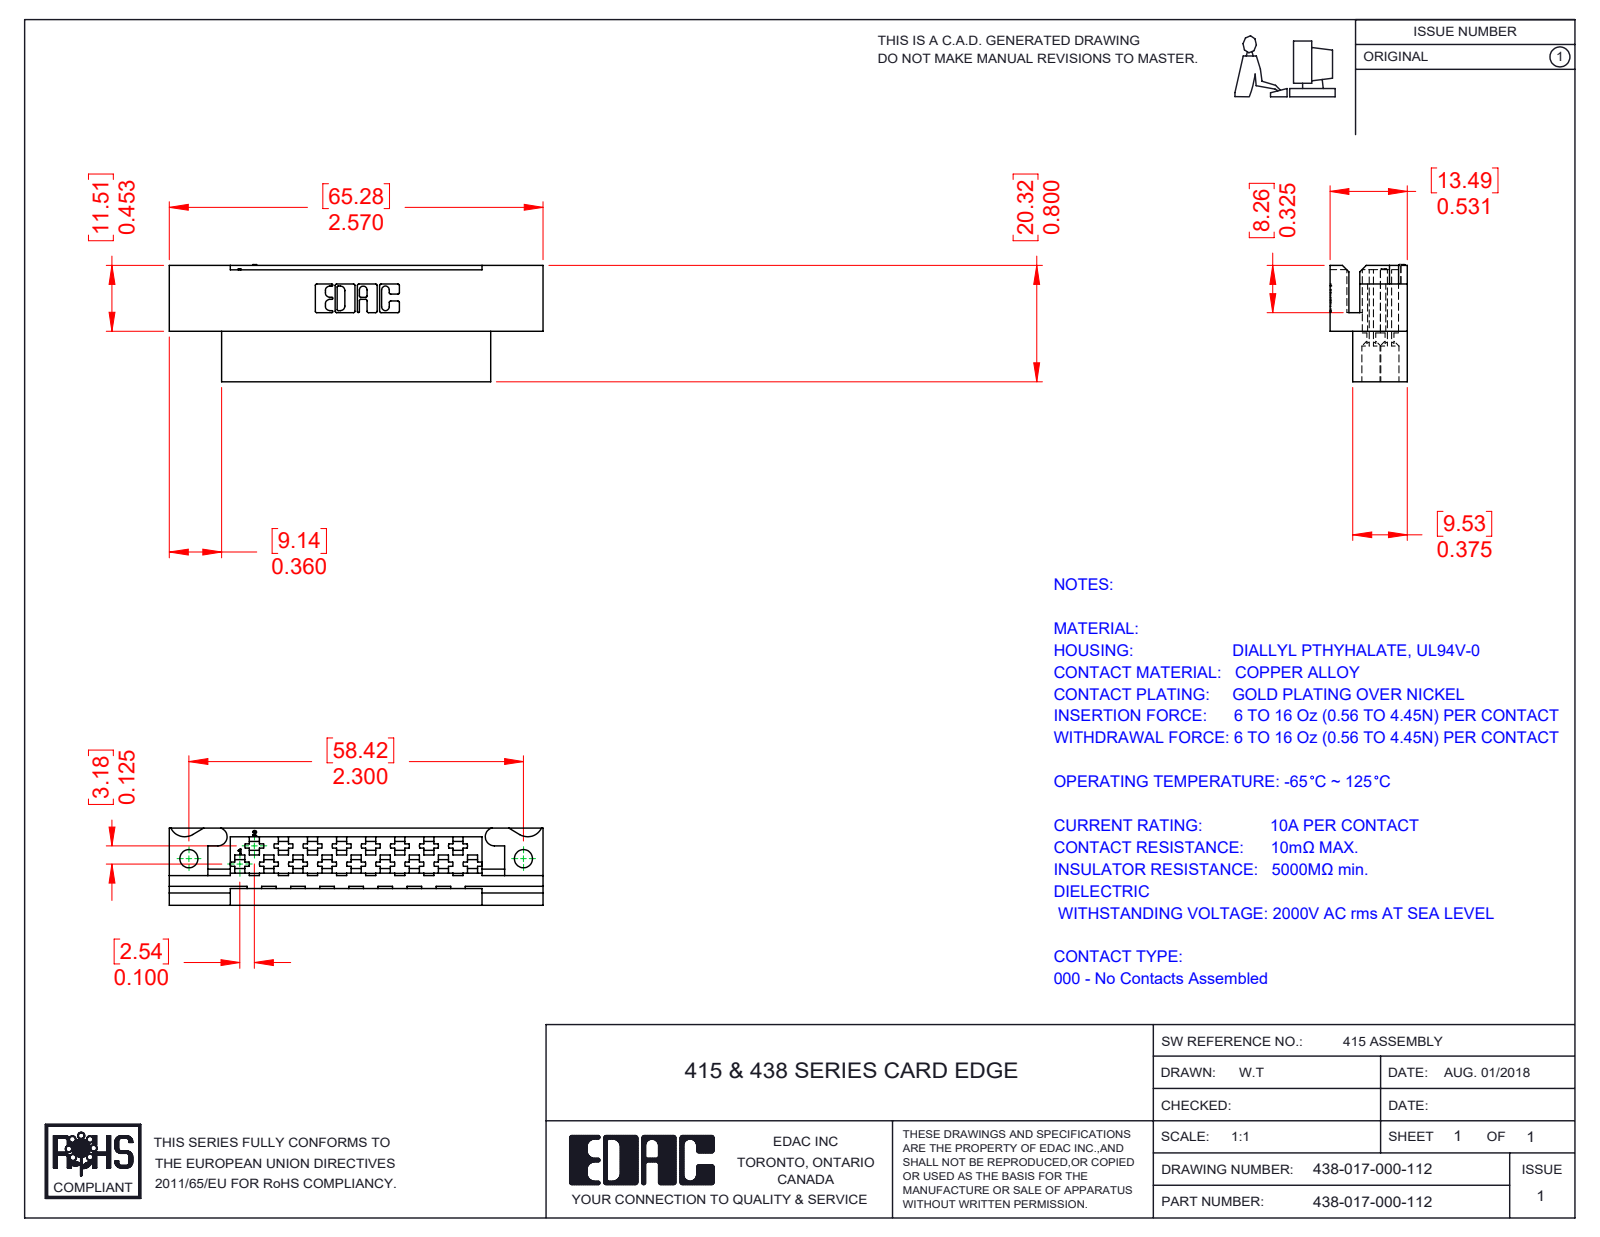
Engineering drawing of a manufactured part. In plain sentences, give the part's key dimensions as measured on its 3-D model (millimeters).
The part is named "438-017-000-112; 438-210-001_438-210-017-112". Its 3-D file was written by "SolidWorks 2016 (CONFIG_CONTROL_DESIGN)". It is 1 solid with 598 faces: 441 planar, 84 cylindrical and 73 other. Overall it measures 65.28 by 20.45 by 13.49 millimeters. Its volume is 9 697 cubic millimeters and its surface area 9 232 square millimeters. Round holes: 17 of diameter 3.3, 1 of diameter 3.17, 1 of diameter 3.18. Partial cylindrical surfaces (rounded edges, fillets, slot ends): 22 of radius 0.25, 6 of radius 0.17, 6 of radius 0.8, 3 of radius 0.67, 2 of radius 1.59, 2 of radius 2.7. The main face-to-face distances are 13.49, 9.53, 3.96, 3.18, 20.32, 3.17, 5.08, 1.23, 4.38, 1.2. The hole center spacings are 4.06, 5.08, 8.25, 10.16, 13.09, 15.24, 18.06, 20.32.
